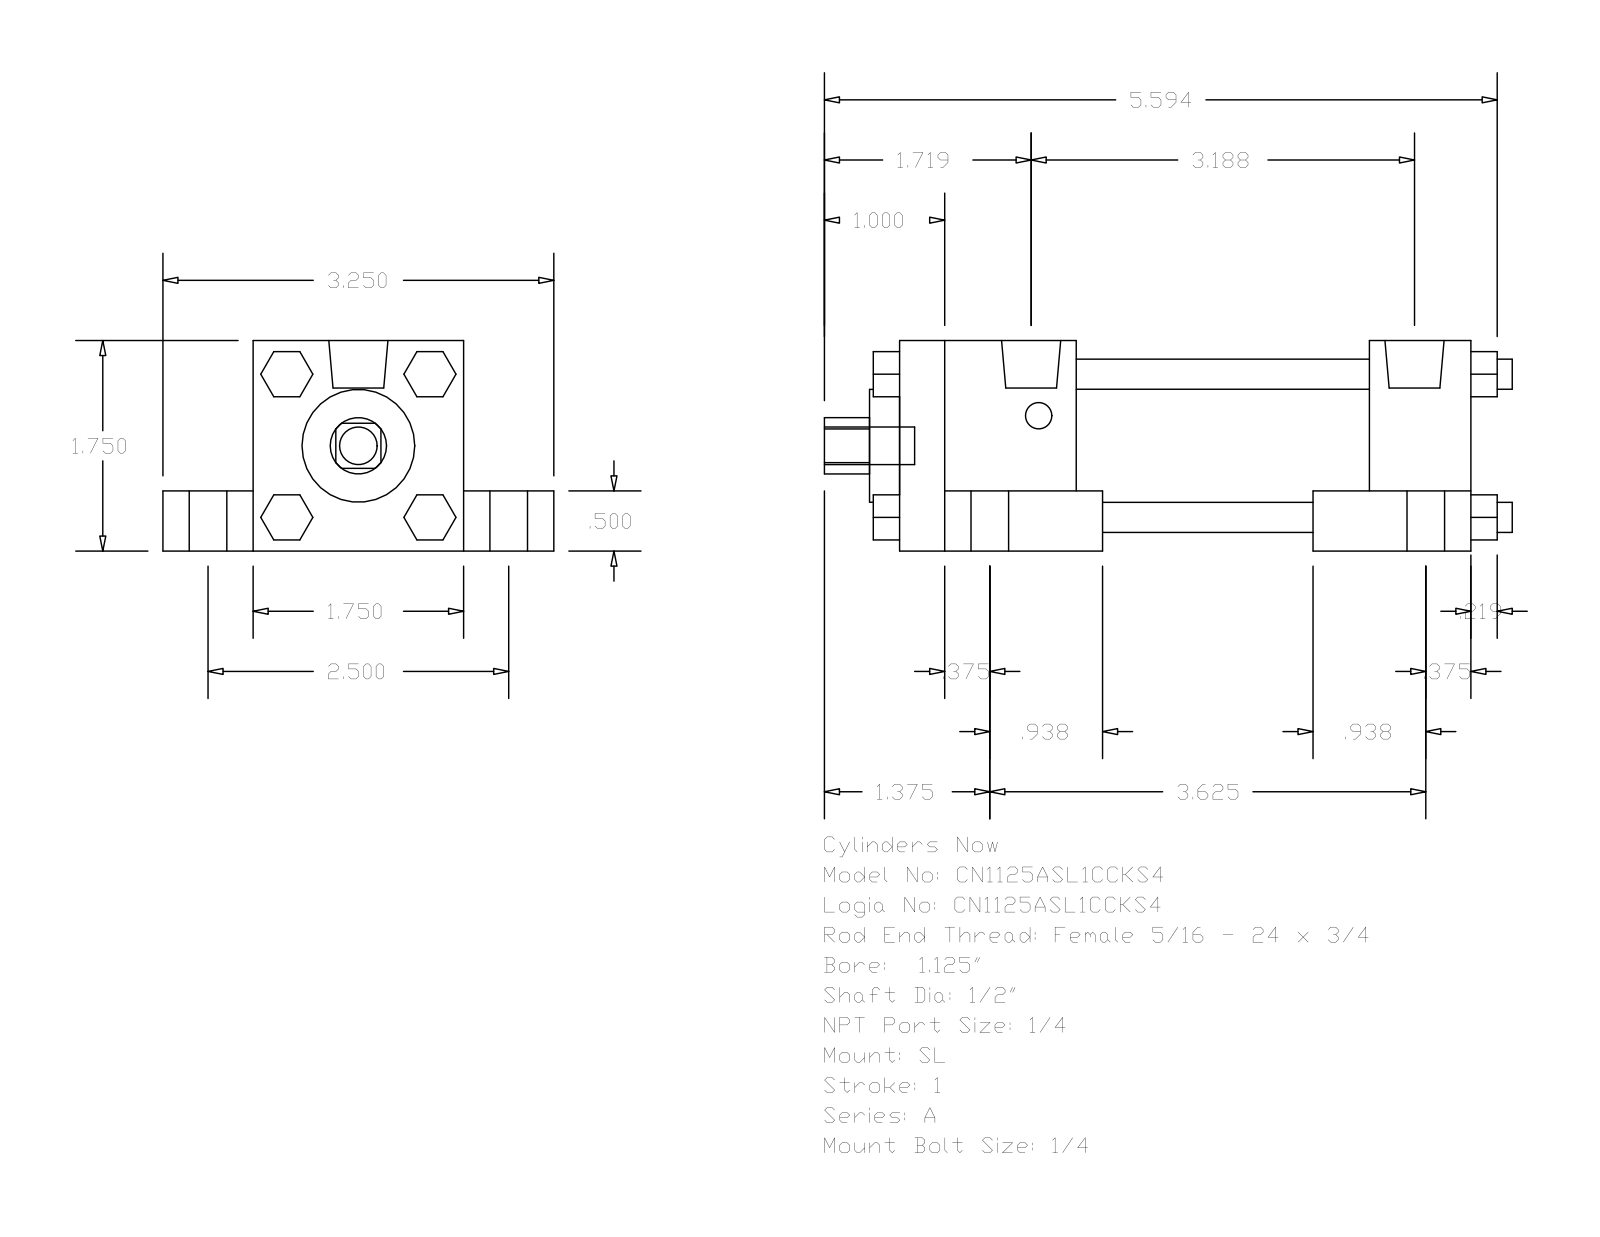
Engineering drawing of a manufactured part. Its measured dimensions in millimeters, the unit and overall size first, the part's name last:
Units: millimetres
Overall size (bounding box): 145.26 × 82.55 × 44.45
Round holes (diameter × count): ⌀12.7 ×1, ⌀23.81 ×1, ⌀31.88 ×1
Round bosses / shafts (diameter × count): ⌀7.94 ×5, ⌀14.29 ×4, ⌀6.35 ×4, ⌀5.56 ×4, ⌀12.49 ×2
Partial cylindrical surfaces — rounded edges, fillets, slot ends (radius × count): R5.94 ×1
Main face-to-face distances: 44.46, 31.76, 12.7, 19.04, 63.5, 120.65, 99.21, 21.44, 37.3, 61.91
Bodies: 0 solids, 150 faces (114 planar, 36 cylindrical, 0 other)
Part name (STEP PRODUCT): A_SL__0112_0.5
STEP written by: GSSL Pune (CONFIG_CONTROL_DESIGN)
